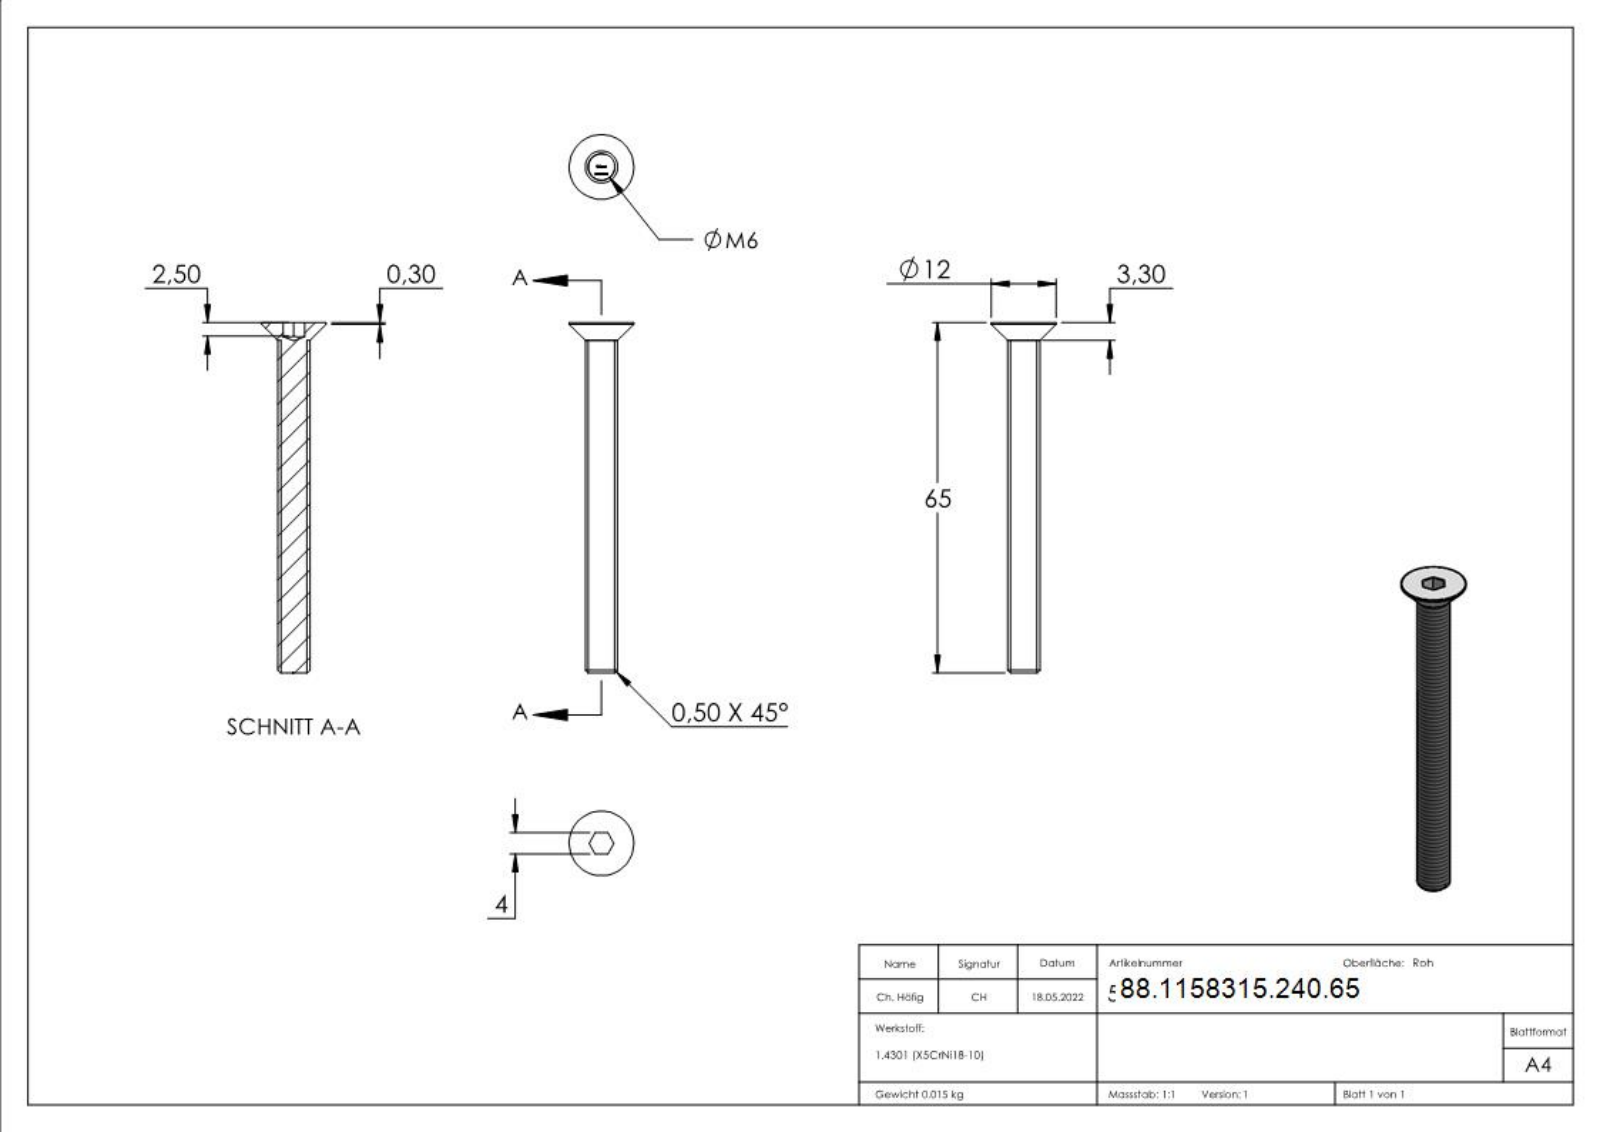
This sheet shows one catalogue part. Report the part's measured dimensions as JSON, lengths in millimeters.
{"part_name": "58315-240-65", "step_written_by": "SolidWorks 2018 (CONFIG_CONTROL_DESIGN)", "units": "millimeters", "bodies": {"solids": 1, "faces": 279, "planar": 147, "cylindrical": 2, "other": 130}, "overall_size": [65, 12, 12], "volume_mm3": 1935, "surface_area_mm2": 1469, "round_bosses_or_shafts": [[12, 1], [6, 1]], "face_to_face_distances": [65, 4, 64.9, 0.8, 0.65, 0.33, 0.82, 0.79, 1.44, 0.59]}
